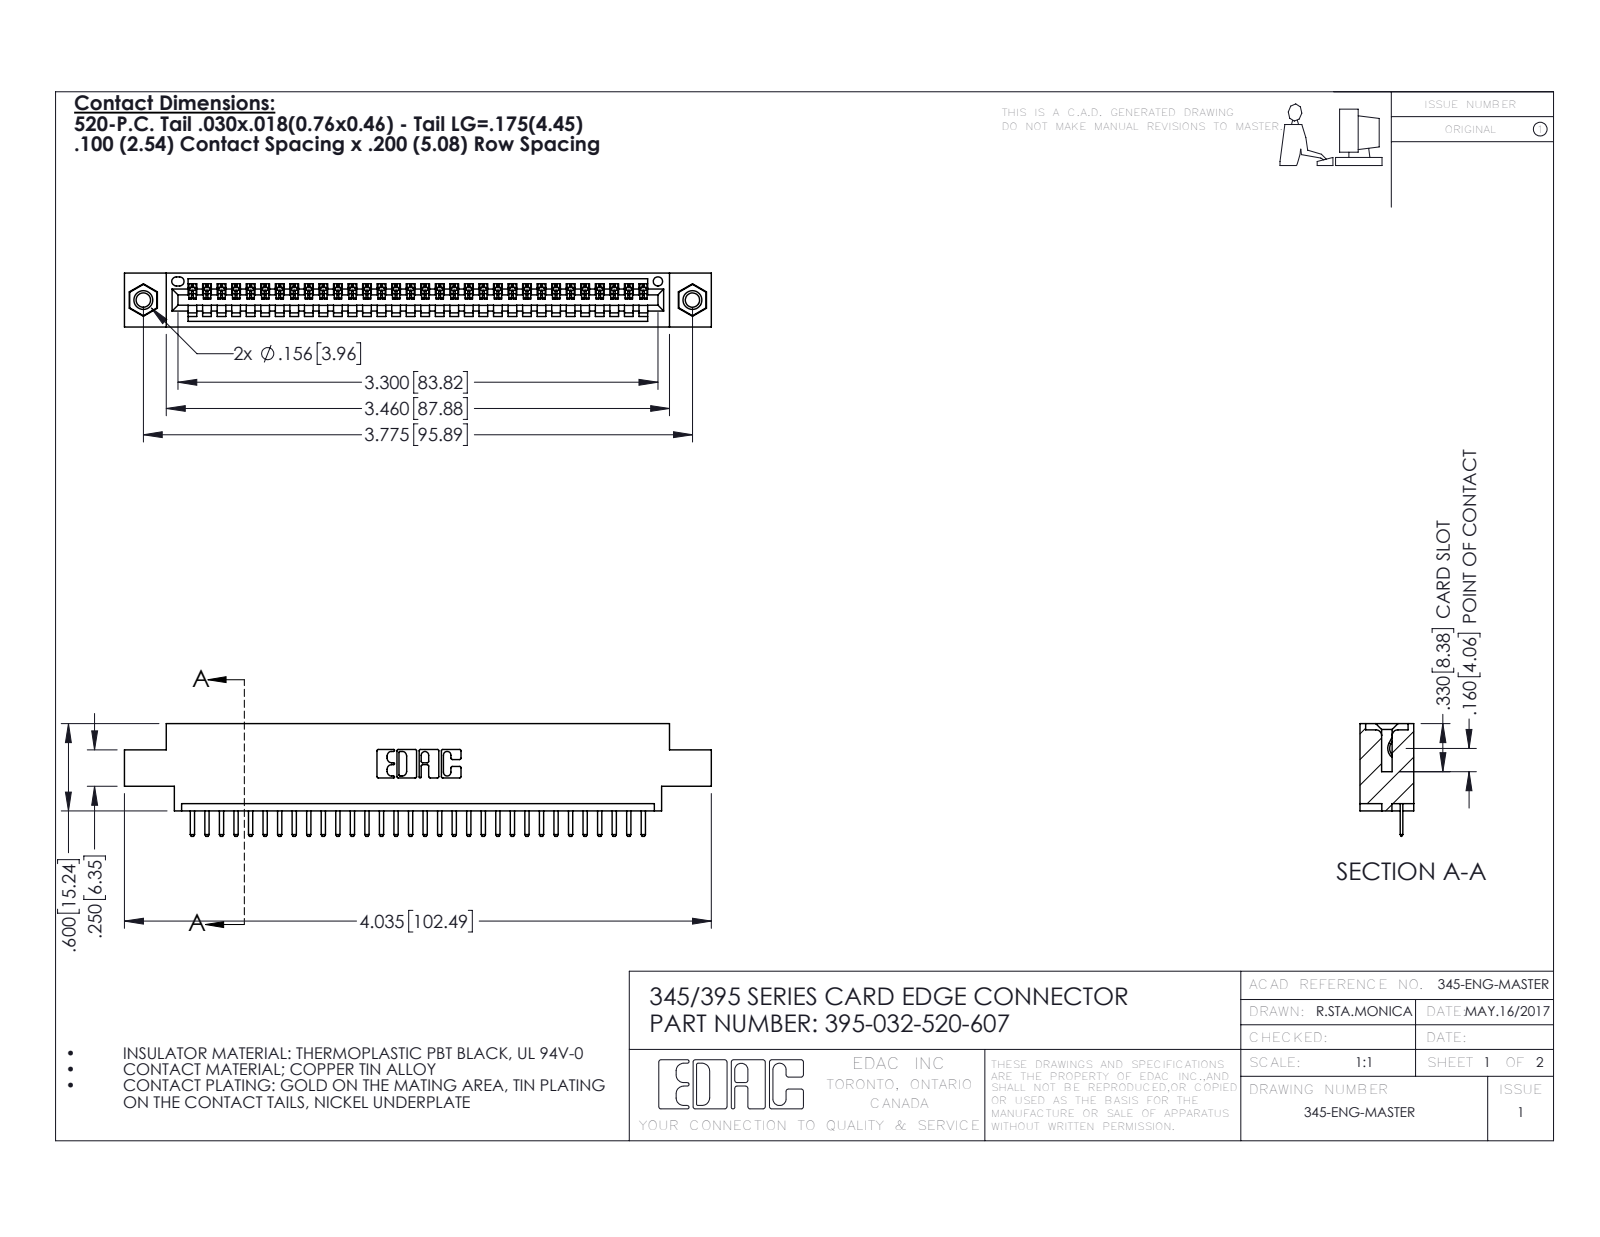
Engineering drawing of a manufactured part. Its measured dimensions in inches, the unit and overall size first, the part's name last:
Units: inches
Overall size (bounding box): 4.035 × 0.775 × 0.37
Round holes (diameter × count): ⌀0.098 ×2, ⌀0.125 ×2, ⌀0.156 ×2, ⌀0.064 ×1
Round bosses / shafts (diameter × count): ⌀0.155 ×2
Partial cylindrical surfaces — rounded edges, fillets, slot ends (radius × count): R0.01 ×66, R0.006 ×64, R0.01 ×22, R0.007 ×6, R0.031 ×6, R0.026 ×3, R0.031 ×2, R0.04 ×2
Main face-to-face distances: 0.072, 0.298, 0.37, 0.2, 0.098, 0.272, 0.025, 0.225, 0.072, 0.175
Hole centre spacings: 0.27, 3.54, 3.775
Volume: 0.576 in³ · Surface area: 19 in²
Bodies: 35 solids, 2174 faces (1460 planar, 698 cylindrical, 16 other)
Part name (STEP PRODUCT): 345-250-001_345-250-005-103; 345 Part_0.170 Offset - 0.156 Dia-TI; 345-292-001_345-293-120; 395-032-520-607
STEP written by: SolidWorks 2016 (CONFIG_CONTROL_DESIGN)
